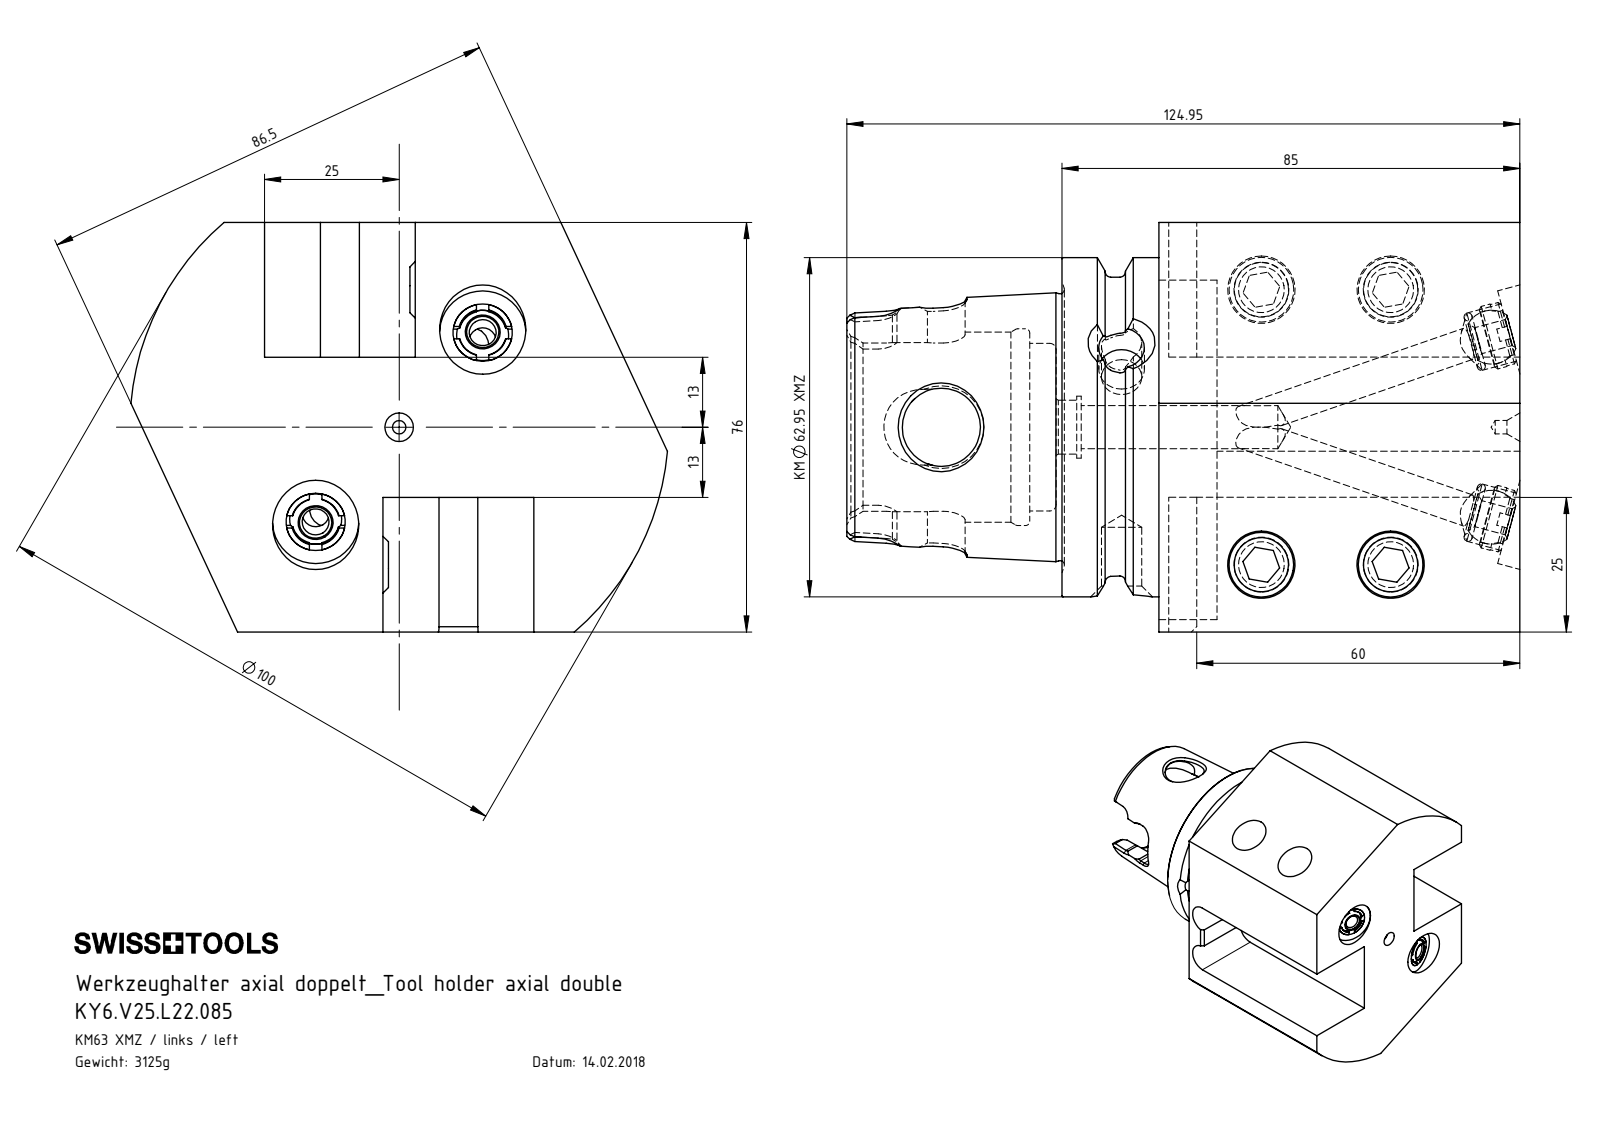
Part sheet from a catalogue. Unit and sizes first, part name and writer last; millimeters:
Units: millimetres
Overall size (bounding box): 124.95 × 99.6 × 76
Round holes (diameter × count): ⌀10.2 ×4, ⌀12.5 ×4, ⌀10 ×3, ⌀5 ×2, ⌀6 ×2, ⌀7.47 ×2, ⌀11 ×2, ⌀16 ×2, ⌀2.5 ×1, ⌀8 ×1, ⌀8.48 ×1, ⌀11.5 ×1
Round bosses / shafts (diameter × count): ⌀12 ×6, ⌀62.95 ×1, ⌀55.7 ×1
Partial cylindrical surfaces — rounded edges, fillets, slot ends (radius × count): R4 ×6, R5.2 ×4, R4.4 ×2, R7.04 ×2, R50 ×1
Main face-to-face distances: 25, 51, 28, 67, 22, 86.46, 76, 6, 26, 50
Hole centre spacings: 24, 51, 56.36, 64.64, 87.21
Volume: 398 155 mm³ · Surface area: 65 785 mm²
Bodies: 11 solids, 397 faces (122 planar, 109 cylindrical, 166 other)
Part name (STEP PRODUCT): KY6-V25.L22.085_B; KU1-U12.002.010_A; DIN 3771 - 8x1.5; ISO 4026 - M12 x 20 (+3 more)
STEP written by: SolidWorks 2017 (CONFIG_CONTROL_DESIGN)
